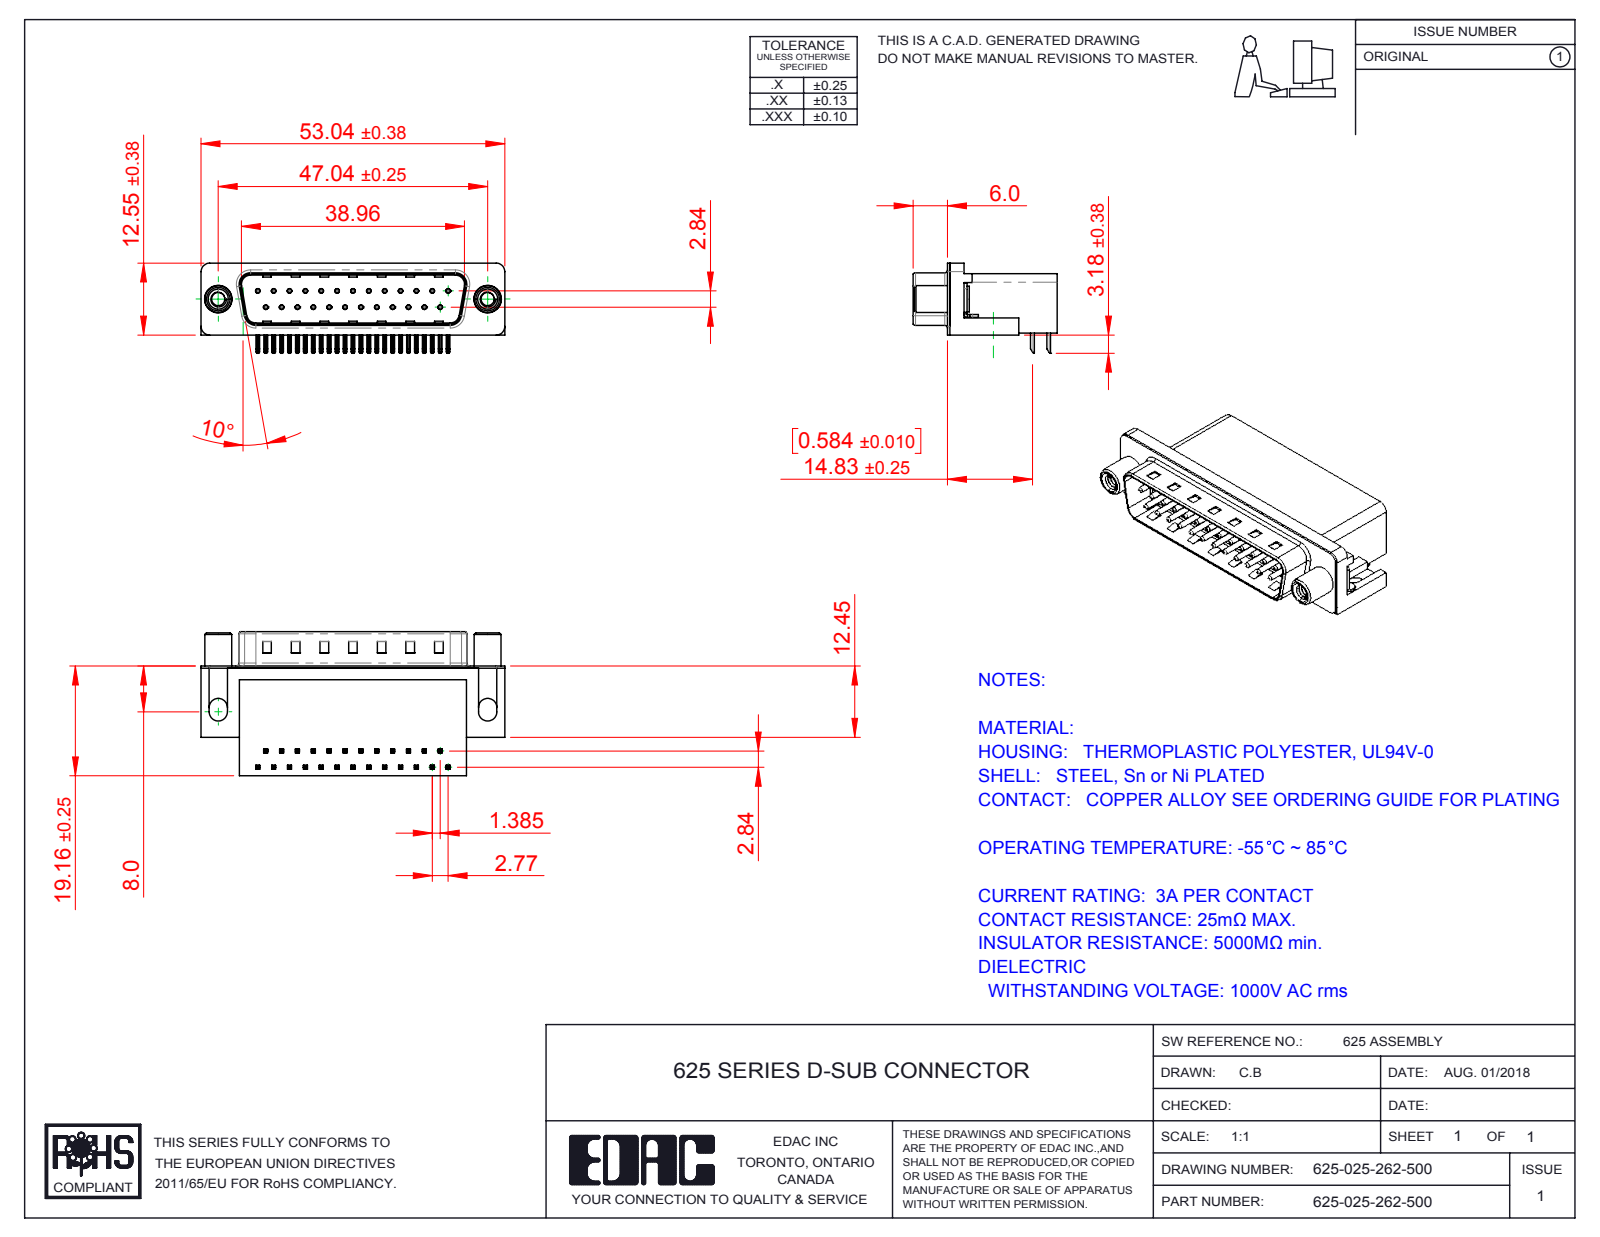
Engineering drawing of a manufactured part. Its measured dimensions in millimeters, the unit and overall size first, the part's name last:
Units: millimetres
Overall size (bounding box): 53.04 × 25.16 × 15.73
Round holes (diameter × count): ⌀0.35 ×25, ⌀0.8 ×25, ⌀2.3 ×2, ⌀3.1 ×2, ⌀4 ×2, ⌀4.8 ×2, ⌀5 ×2
Round bosses / shafts (diameter × count): ⌀0.75 ×25, ⌀4.9 ×2, ⌀4.7 ×2, ⌀4.5 ×2, ⌀3.85 ×2
Partial cylindrical surfaces — rounded edges, fillets, slot ends (radius × count): R0.25 ×100, R0.12 ×50, R1 ×16, R0.5 ×9, R1.6 ×8, R1.5 ×7, R0.9 ×4, R2 ×4
Main face-to-face distances: 0.4, 10.35, 18.76, 2.1, 8.76, 10.46, 10.86, 1.7, 19.16, 2.9
Hole centre spacings: 3.16, 2.77, 11.08, 5.54, 8.31, 5.03, 13.85, 7.48
Volume: 9 227 mm³ · Surface area: 8 927 mm²
Bodies: 31 solids, 2257 faces (1399 planar, 665 cylindrical, 193 other)
Part name (STEP PRODUCT): 625-025-262-500; 625 Housing_25 Socket; 625 Shell_25 Socket; 625 Round Threaded Standoff (+3 more)
STEP written by: SolidWorks 2016 (CONFIG_CONTROL_DESIGN)
